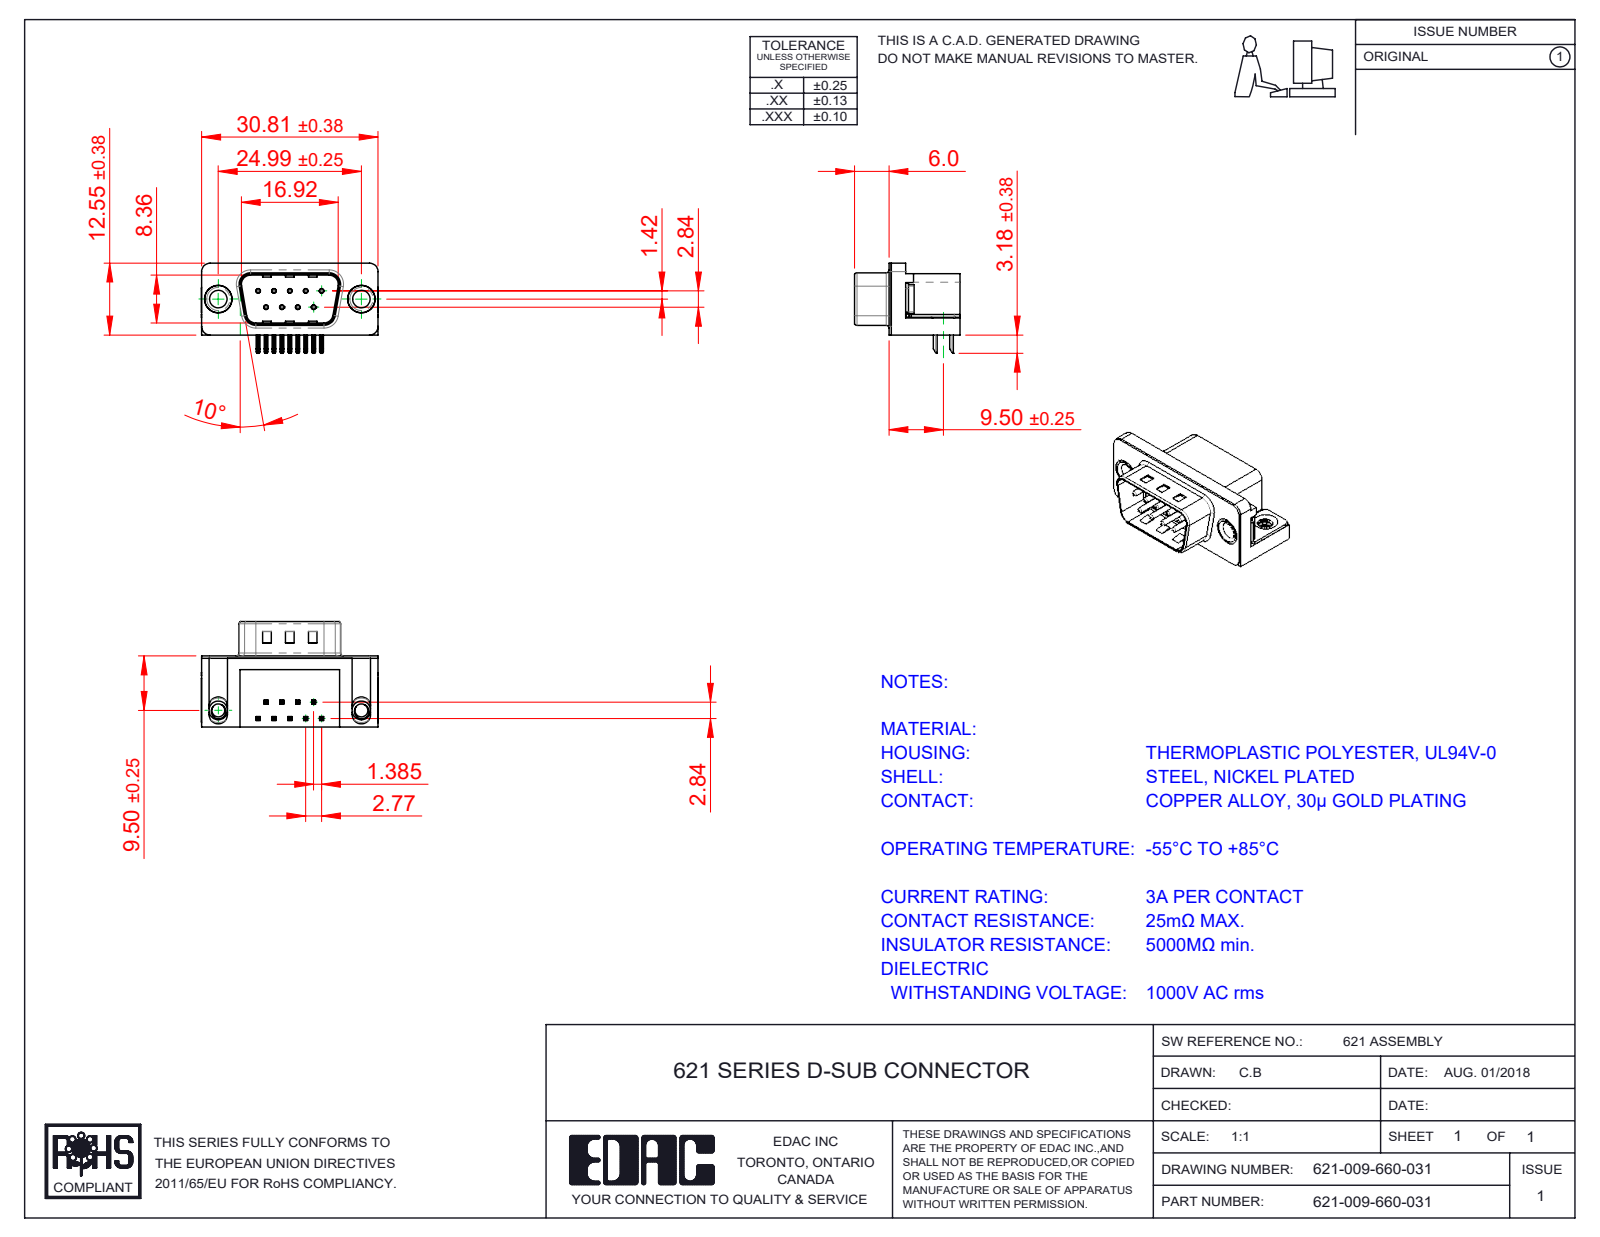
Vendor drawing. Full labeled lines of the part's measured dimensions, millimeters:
Part name (STEP PRODUCT): 621 Thru Hole Rivet; 621-009-660-031; 621 Housing_9 Socket; 621 Contact Top (+3 more)
STEP written by: SolidWorks 2016 (CONFIG_CONTROL_DESIGN)
Units: millimetres
Bodies: 15 solids, 991 faces (605 planar, 305 cylindrical, 81 other)
Overall size (bounding box): 30.89 × 18.4 × 16.25
Volume: 3 233 mm³ · Surface area: 4 403 mm²
Round holes (diameter × count): ⌀0.35 ×9, ⌀0.8 ×9, ⌀3.05 ×2, ⌀4 ×2, ⌀4.8 ×2, ⌀5 ×2
Round bosses / shafts (diameter × count): ⌀0.75 ×9, ⌀4.9 ×2, ⌀4.75 ×2, ⌀3.85 ×2
Partial cylindrical surfaces — rounded edges, fillets, slot ends (radius × count): R0.25 ×44, R0.12 ×18, R1 ×16, R0.5 ×14, R1.5 ×8, R1.6 ×8, R0.32 ×4, R0.9 ×4
Main face-to-face distances: 0.4, 12, 12.4, 10.35, 0.5, 9.5, 2.5, 2.9, 2.1, 0.35
Hole centre spacings: 3.16, 2.77, 5.54, 5.03, 5.04, 8.31, 7.48, 7.49
